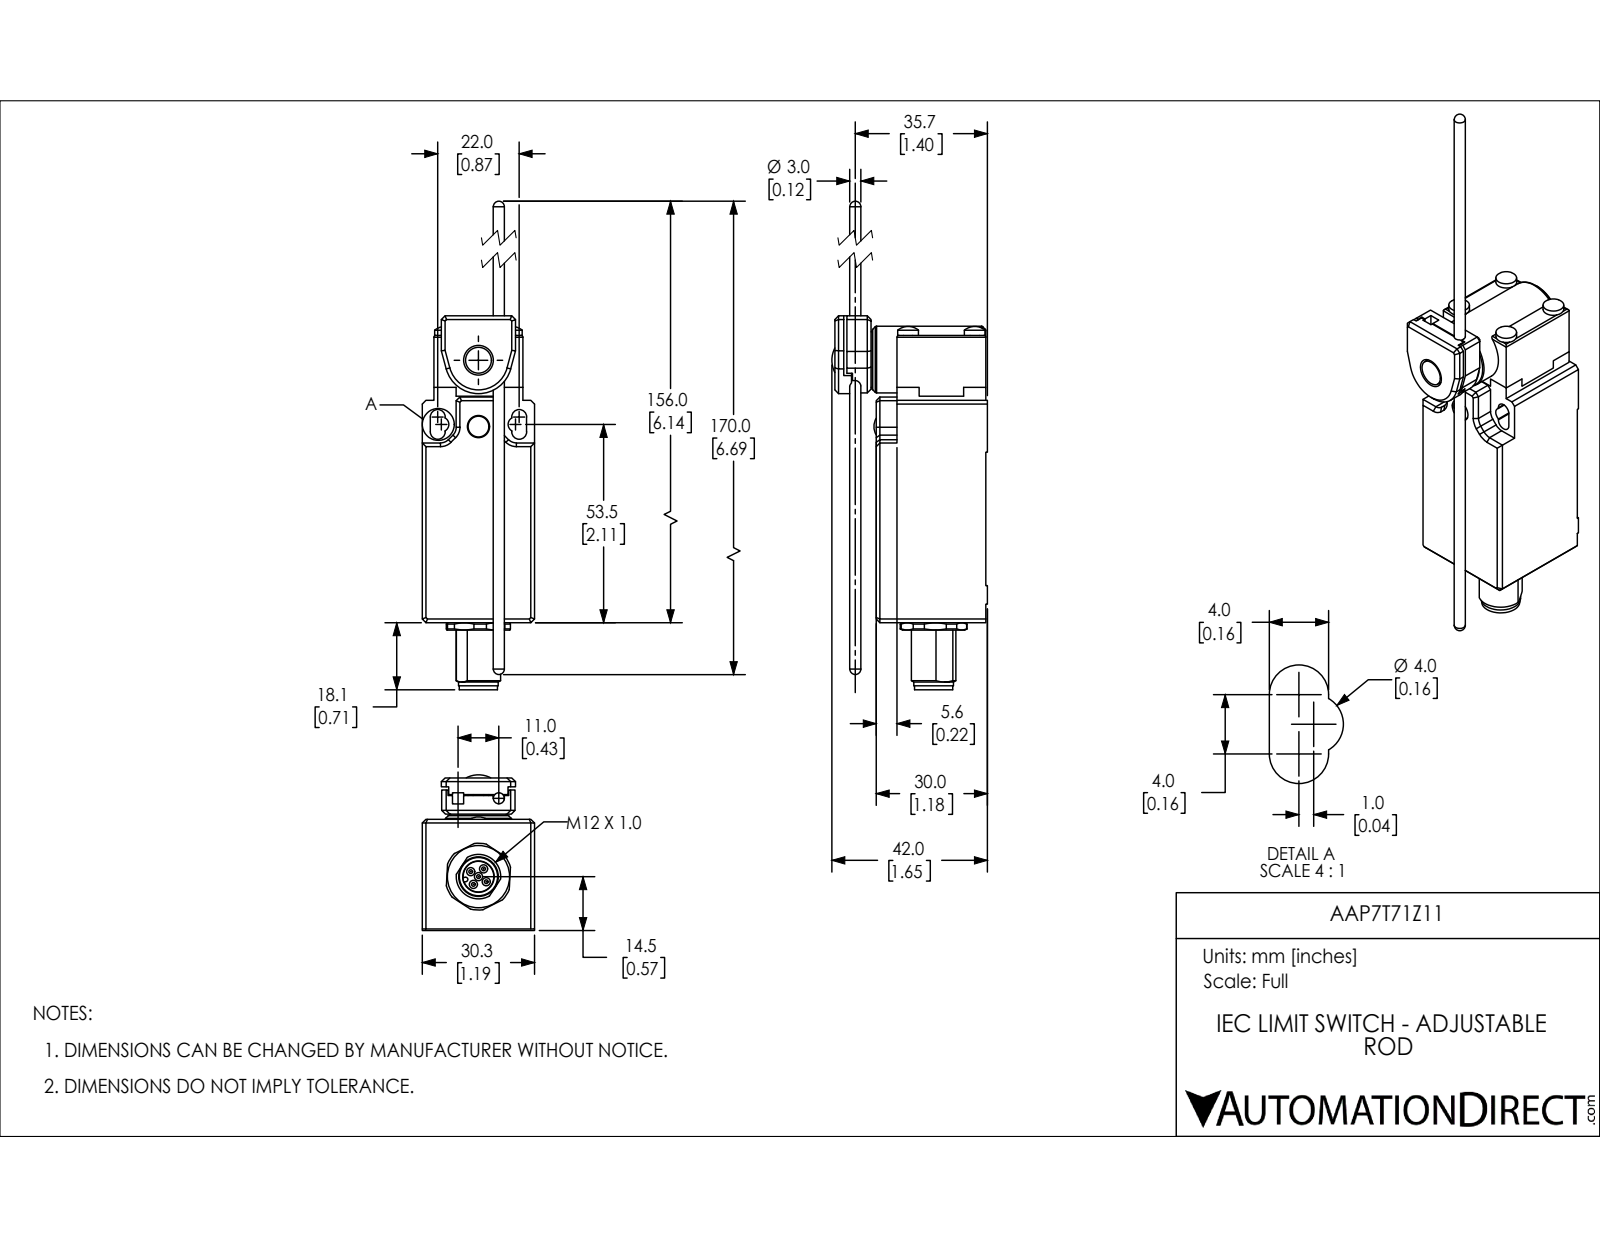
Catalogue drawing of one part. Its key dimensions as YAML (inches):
part_name: "AAP7T71Z11"
step_written_by: "SolidWorks 2018 (AUTOMOTIVE_DESIGN)"
units: inches
bodies: {solids: 5, faces: 393, planar: 203, cylindrical: 126, other: 64}
overall_size: [6.854, 1.652, 1.193]
volume: 4.292
surface_area: 31.28
round_holes:
  - {diameter: 0.087, count: 5}
  - {diameter: 0.118, count: 1}
  - {diameter: 0.236, count: 1}
  - {diameter: 0.315, count: 1}
  - {diameter: 0.433, count: 1}
  - {diameter: 0.512, count: 1}
  - {diameter: 0.551, count: 1}
  - {diameter: 0.63, count: 1}
round_bosses_or_shafts:
  - {diameter: 0.22, count: 5}
  - {diameter: 0.055, count: 5}
  - {diameter: 0.039, count: 5}
  - {diameter: 0.709, count: 1}
  - {diameter: 0.591, count: 1}
  - {diameter: 0.421, count: 1}
  - {diameter: 0.406, count: 1}
  - {diameter: 0.276, count: 1}
partial_cylinders:
  - {radius: 0.079, count: 6}
  - {radius: 0.02, count: 4}
  - {radius: 0.118, count: 4}
  - {radius: 0.354, count: 2}
  - {radius: 0.024, count: 1}
  - {radius: 0.181, count: 1}
  - {radius: 0.236, count: 1}
  - {radius: 0.252, count: 1}
face_to_face_distances: [1.193, 1.165, 0.124, 1.069, 0.945, 2.406, 0.276, 1.181, 0.016, 0.039]
hole_center_spacings: [0.098, 0.139, 0.197, 0.705, 0.713, 0.768, 0.834, 0.86]
